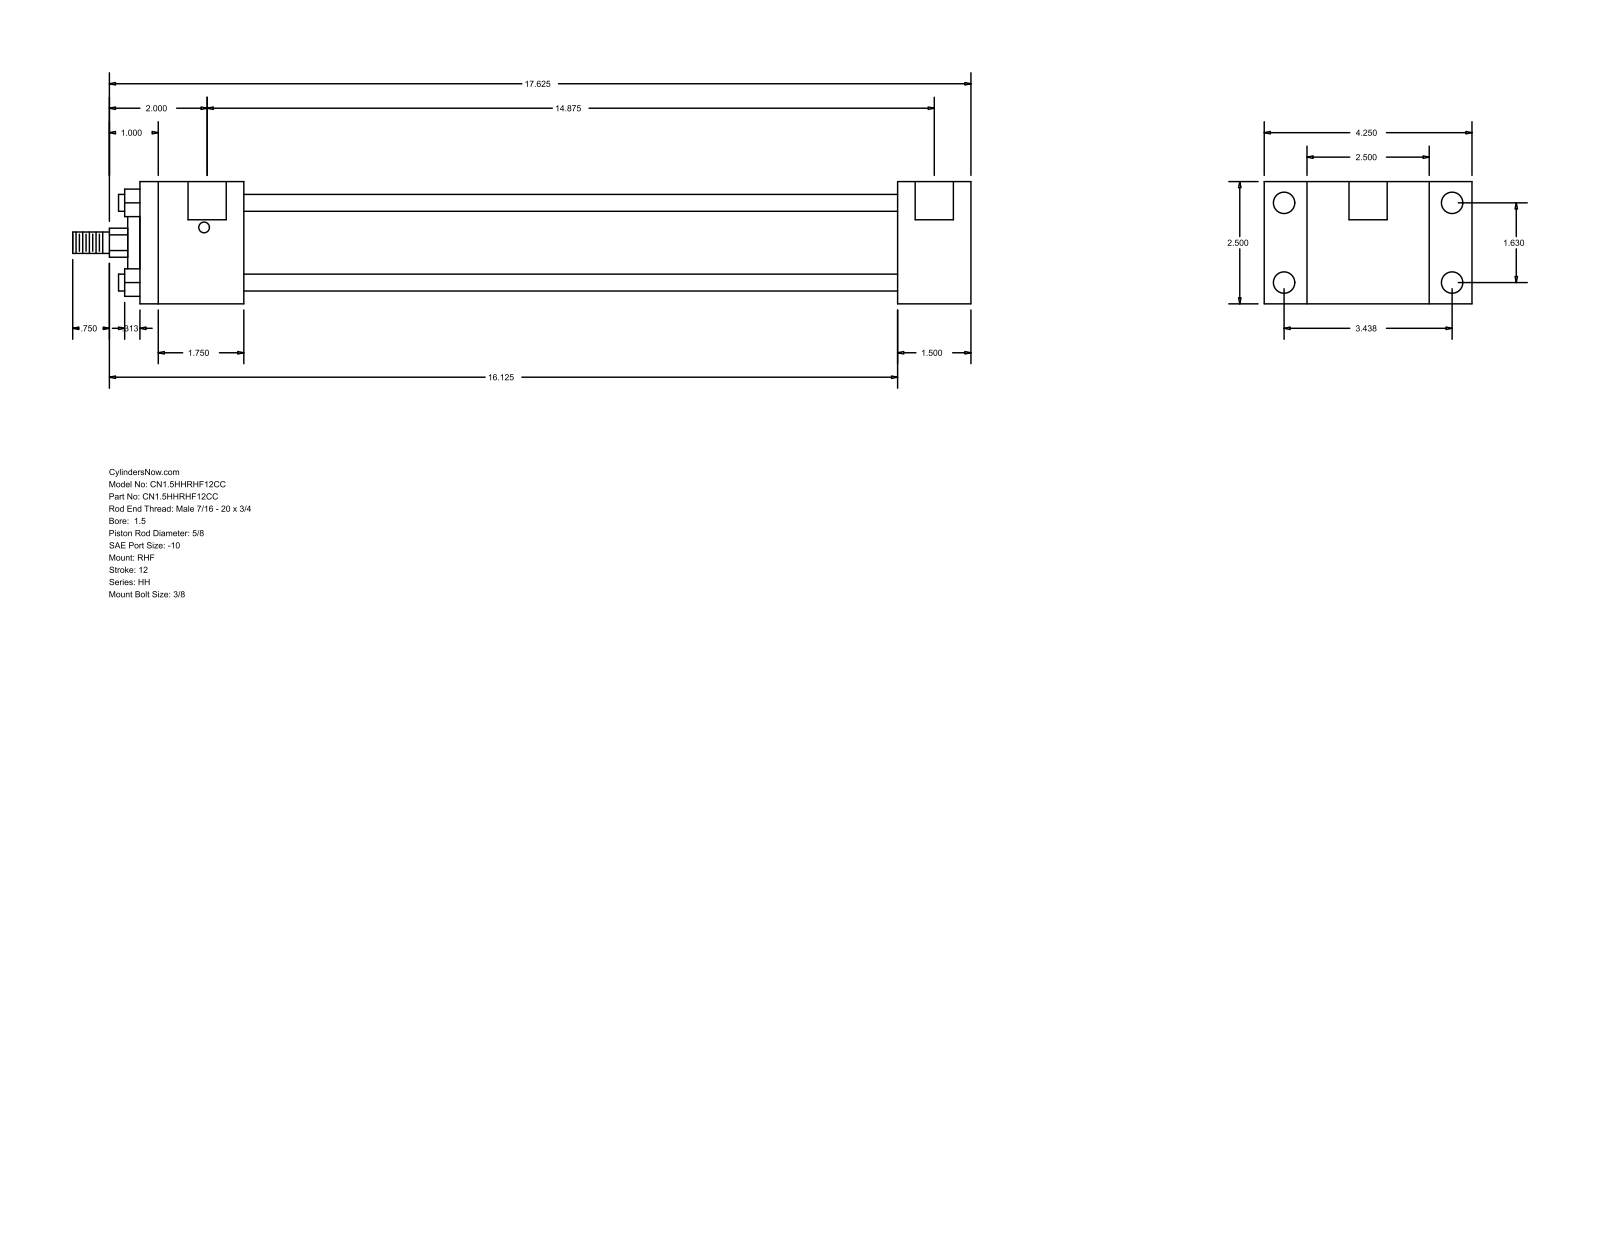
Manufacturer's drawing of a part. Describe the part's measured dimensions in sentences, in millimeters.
The part is named "HH_RHF__0150_0.625". Its 3-D file was written by "GSSL Pune (CONFIG_CONTROL_DESIGN)". It is 0 solids with 88 faces: 60 planar, 28 cylindrical and 0 other. Overall it measures 466.73 by 107.95 by 63.5 millimeters. Round holes: 4 of diameter 5.56, 4 of diameter 11.13, 2 of diameter 19.84. Round bosses or shafts: 4 of diameter 8.76, 1 of diameter 44.45, 1 of diameter 28.57, 1 of diameter 15.88, 1 of diameter 11.11. Partial cylindrical surfaces (rounded edges, fillets, slot ends): 1 of radius 7.54. The main face-to-face distances are 63.5, 22.23, 85.73, 38.11, 393.69, 431.8, 107.96, 53.97, 339.72, 377.83. The hole center spacings are 1.59, 41.4, 87.32, 96.64, 379.41, 381, 377.82.
